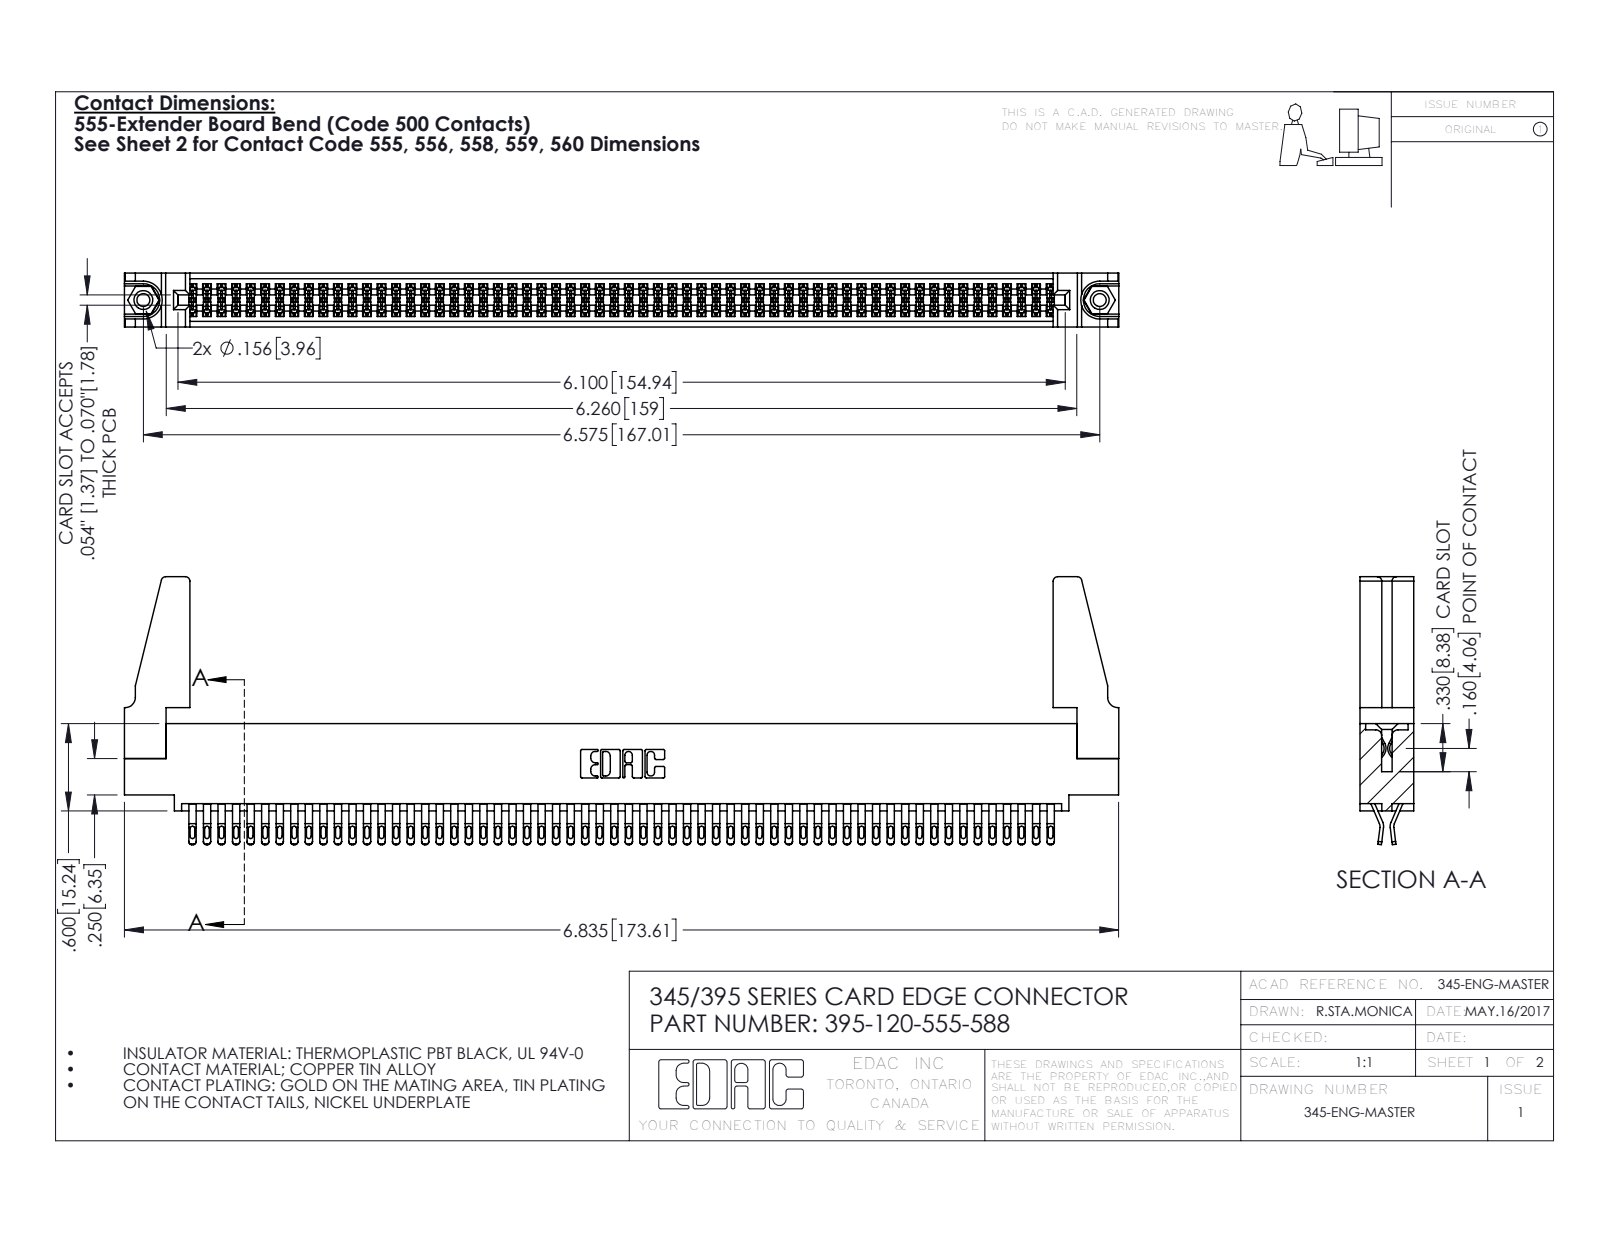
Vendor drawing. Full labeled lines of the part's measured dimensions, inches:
Part name (STEP PRODUCT): 395-120-555-588; 345-250-001_345-250-001-102; 345-292-001_555 Tail; 345 Part_0.110 Offset - 0.156 Dia-TH (+1 more)
STEP written by: SolidWorks 2016 (CONFIG_CONTROL_DESIGN)
Units: inches
Bodies: 125 solids, 6974 faces (3876 planar, 3082 cylindrical, 16 other)
Overall size (bounding box): 6.836 × 1.842 × 0.37
Volume: 1.255 in³ · Surface area: 47.06 in²
Round holes (diameter × count): ⌀0.089 ×2, ⌀0.125 ×2, ⌀0.156 ×2, ⌀0.064 ×1
Round bosses / shafts (diameter × count): ⌀0.155 ×2
Partial cylindrical surfaces — rounded edges, fillets, slot ends (radius × count): R0.016 ×300, R0.02 ×240, R0.006 ×180, R0.01 ×22, R0.03 ×8, R0.007 ×6, R0.031 ×6, R0.026 ×3
Main face-to-face distances: 0.072, 0.298, 0.37, 0.025, 0.2, 0.098, 0.272, 0.225, 0.175, 0.149
Hole centre spacings: 0.27, 6.339, 6.575
